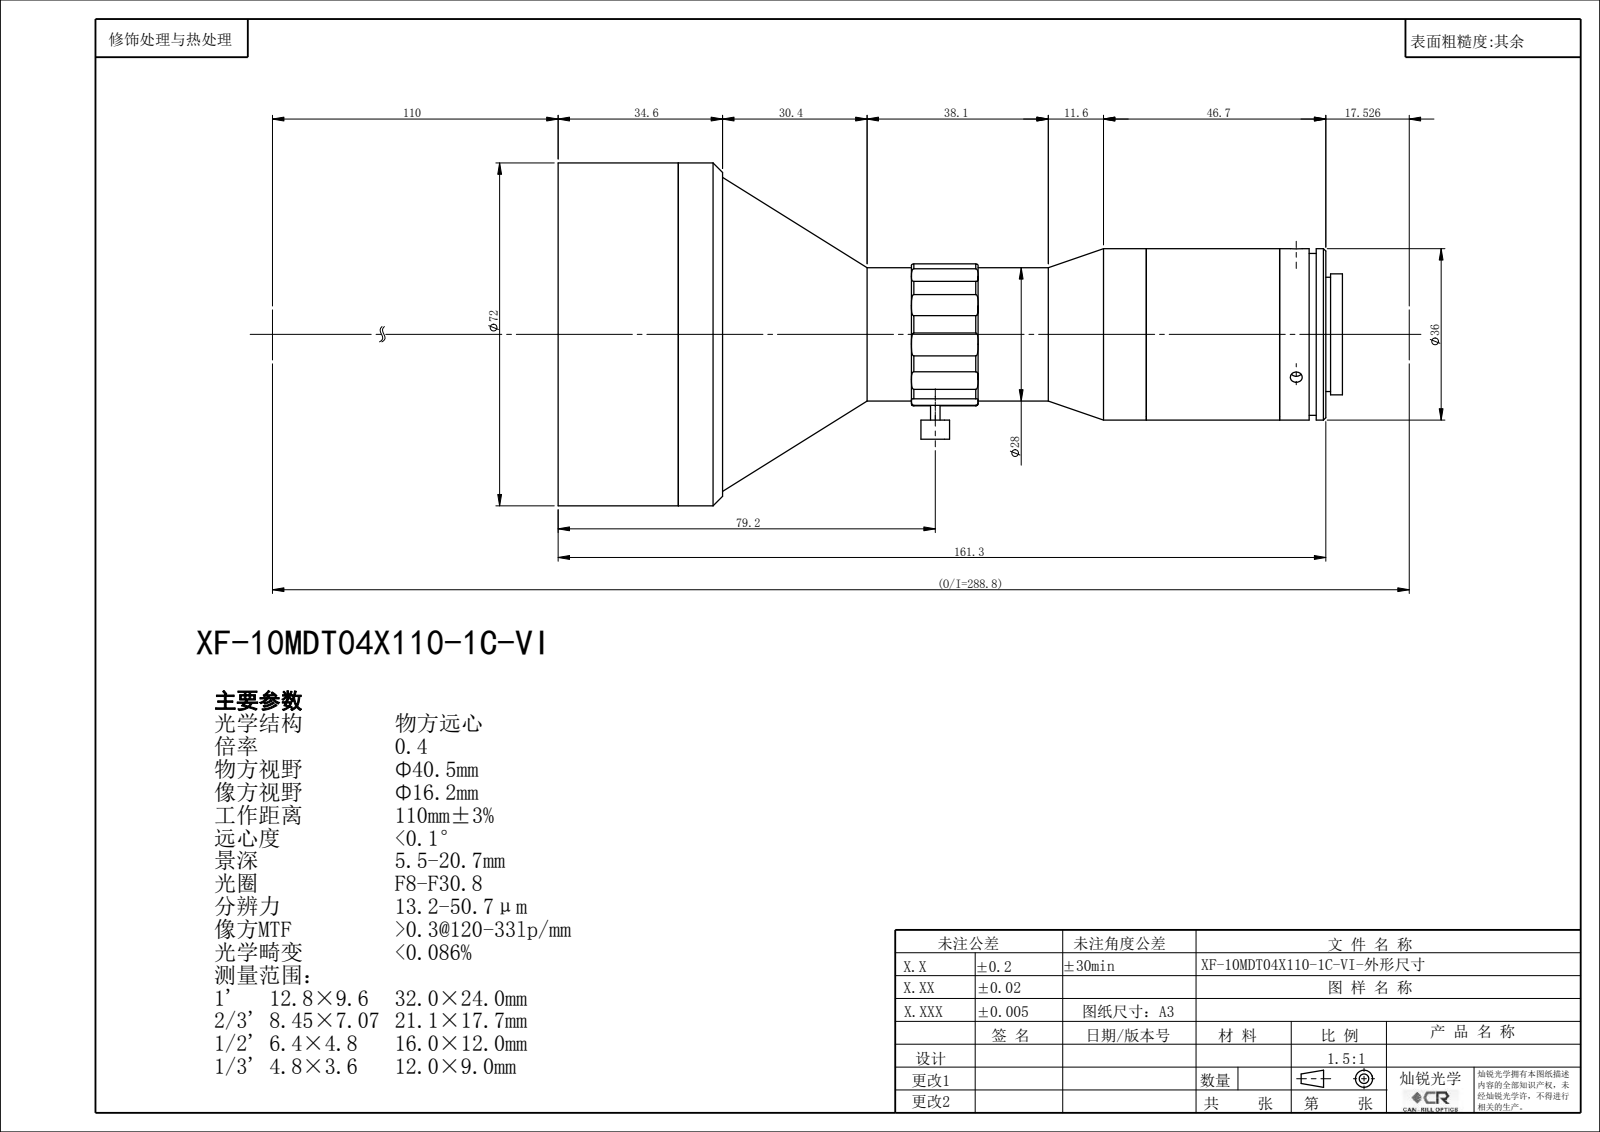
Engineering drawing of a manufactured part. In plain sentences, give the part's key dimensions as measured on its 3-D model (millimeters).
The part is named "XF-5MDT04X110-1C-VI". Its 3-D file was written by "SolidWorks 2014 (CONFIG_CONTROL_DESIGN)". It is 0 solids with 129 faces: 24 planar, 69 cylindrical and 36 other. Overall it measures 164.77 by 72 by 72 millimeters. Round holes: 3 of diameter 2.5, 1 of diameter 21.4, 1 of diameter 24, 1 of diameter 57, 1 of diameter 62, 1 of diameter 66. Round bosses or shafts: 1 of diameter 72, 1 of diameter 36, 1 of diameter 34, 1 of diameter 28, 1 of diameter 25.4, 1 of diameter 6, 1 of diameter 2. Partial cylindrical surfaces (rounded edges, fillets, slot ends): 11 of radius 10, 1 of radius 15. The main face-to-face distances are 25.25, 5.27, 19.98, 151.57, 146.3, 126.32, 161.27, 156, 136.02, 9.7.
